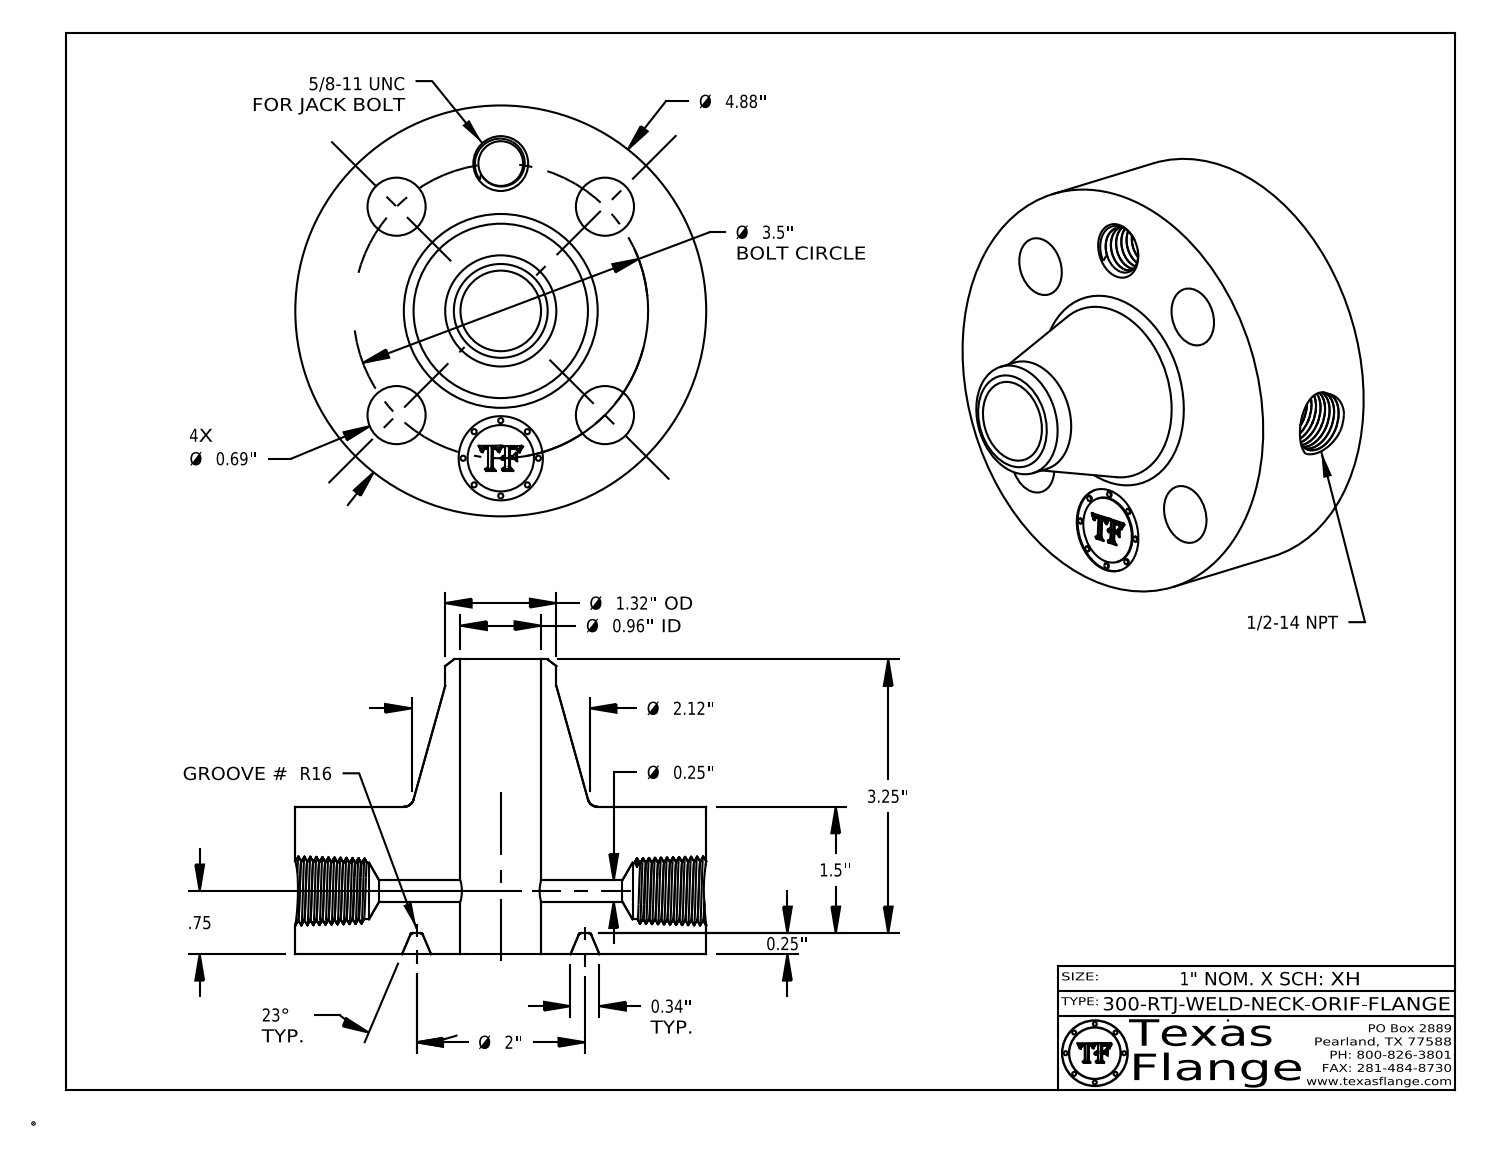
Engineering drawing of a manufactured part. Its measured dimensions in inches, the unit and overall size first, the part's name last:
Units: inches
Overall size (bounding box): 4.88 × 4.88 × 3.5
Round holes (diameter × count): ⌀0.69 ×4, ⌀0.25 ×1, ⌀0.531 ×1, ⌀0.672 ×1, ⌀0.957 ×1, ⌀1 ×1
Round bosses / shafts (diameter × count): ⌀0.061 ×8, ⌀4.88 ×1, ⌀1.32 ×1, ⌀0.788 ×1
Main face-to-face distances: 1.75, 0.25, 1.5, 1.735, 1.485, 0.015, 3.5, 3.25, 1.765, 0.298
Hole centre spacings: 1.75, 1.339, 2.475, 3.233, 3.5
Volume: 29.7 in³ · Surface area: 106.8 in²
Bodies: 1 solid, 789 faces (370 planar, 91 cylindrical, 328 other)
Part name (STEP PRODUCT): 300-RTJ-WELD-NECK
STEP written by: CATIA V5 STEP AP214 (AUTOMOTIVE_DESIGN)
